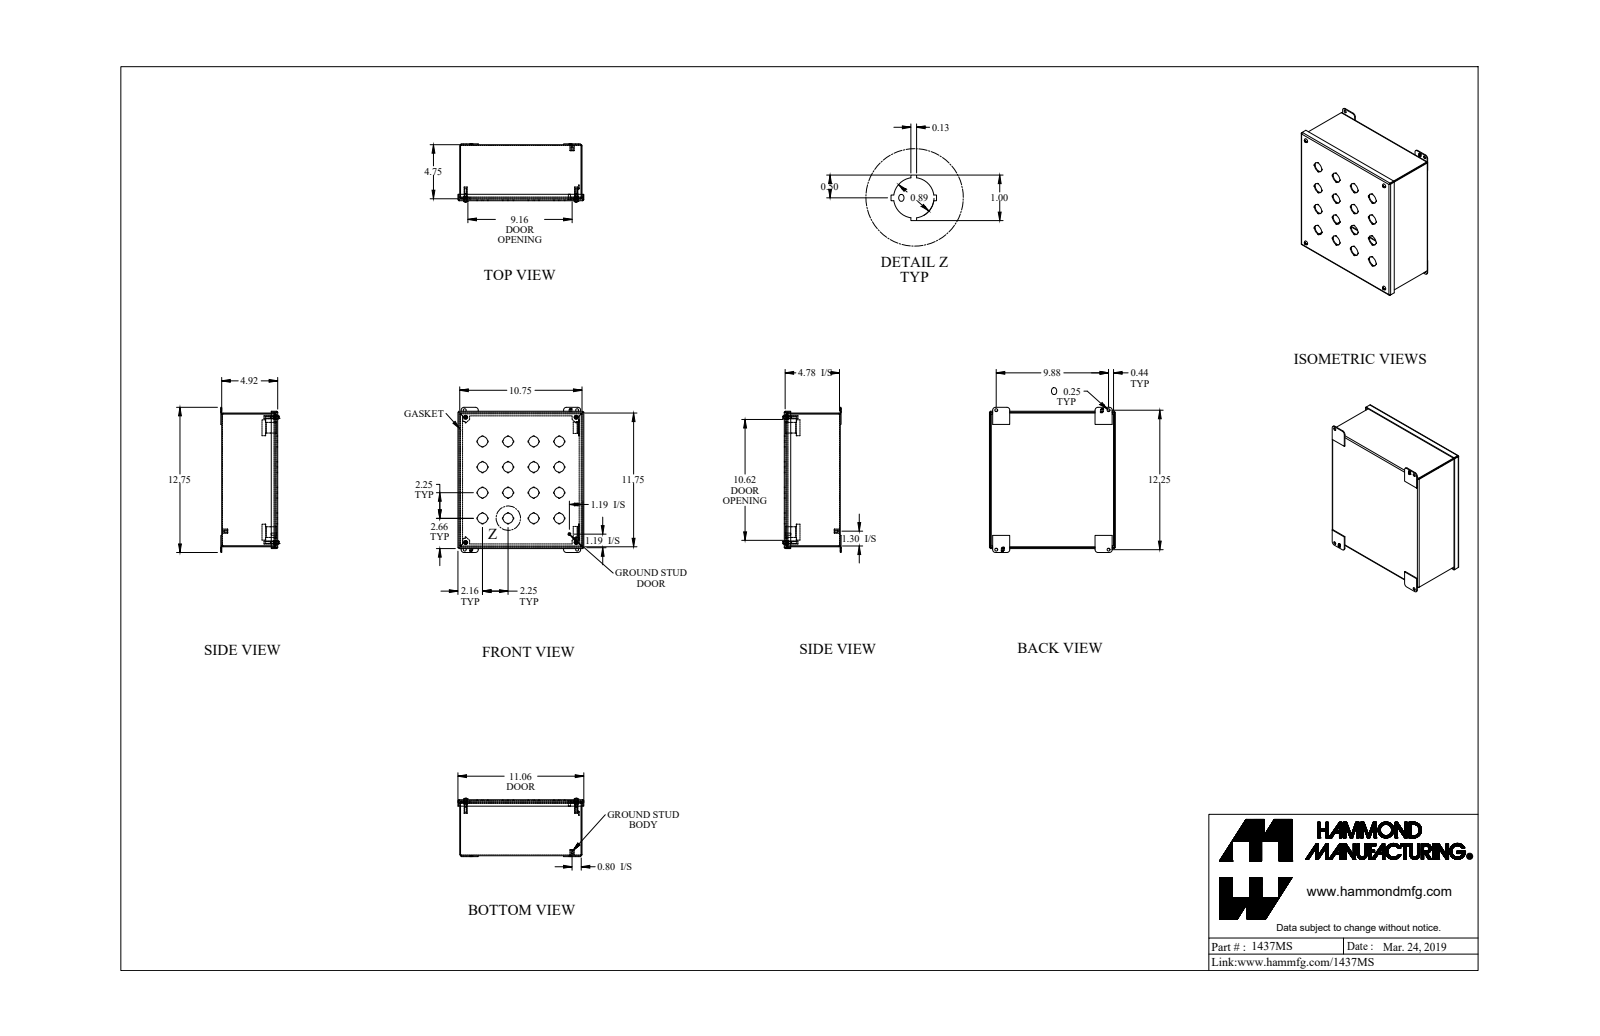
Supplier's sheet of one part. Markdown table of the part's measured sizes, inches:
| quantity | value |
| --- | --- |
| part name | 1437MS_Default |
| STEP written by | SolidWorks 2019 (CONFIG_CONTROL_DESIGN) |
| units | inches |
| bodies | 23 solids, 971 faces (691 planar, 224 cylindrical, 56 other) |
| overall size | 12.75 × 11.062 × 5.121 |
| volume | 40.26 in³ |
| surface area | 1 078 in² |
| round holes (diameter × count) | 0.886 × 16, 0.25 × 8, 0.159 × 4, 0.406 × 4, 0.156 × 1 |
| round bosses / shafts (diameter × count) | 0.39 × 4, 0.275 × 4, 0.19 × 4, 0.148 × 4, 0.375 × 1, 0.25 × 1, 0.188 × 1 |
| partial cylindrical surfaces (radius × count) | 0.036 × 12, 0.108 × 12, 0.25 × 8, 0.029 × 4, 0.086 × 4, 0.16 × 4, 0.171 × 4 |
| main face-to-face distances | 0.072, 4.85, 4.922, 4.778, 10.678, 0.072, 11.678, 10.606, 10.75, 11.75 |
| hole center spacings | 2.25, 5.031, 3.182, 4.5, 7.115, 11, 11.626, 6.364 |
